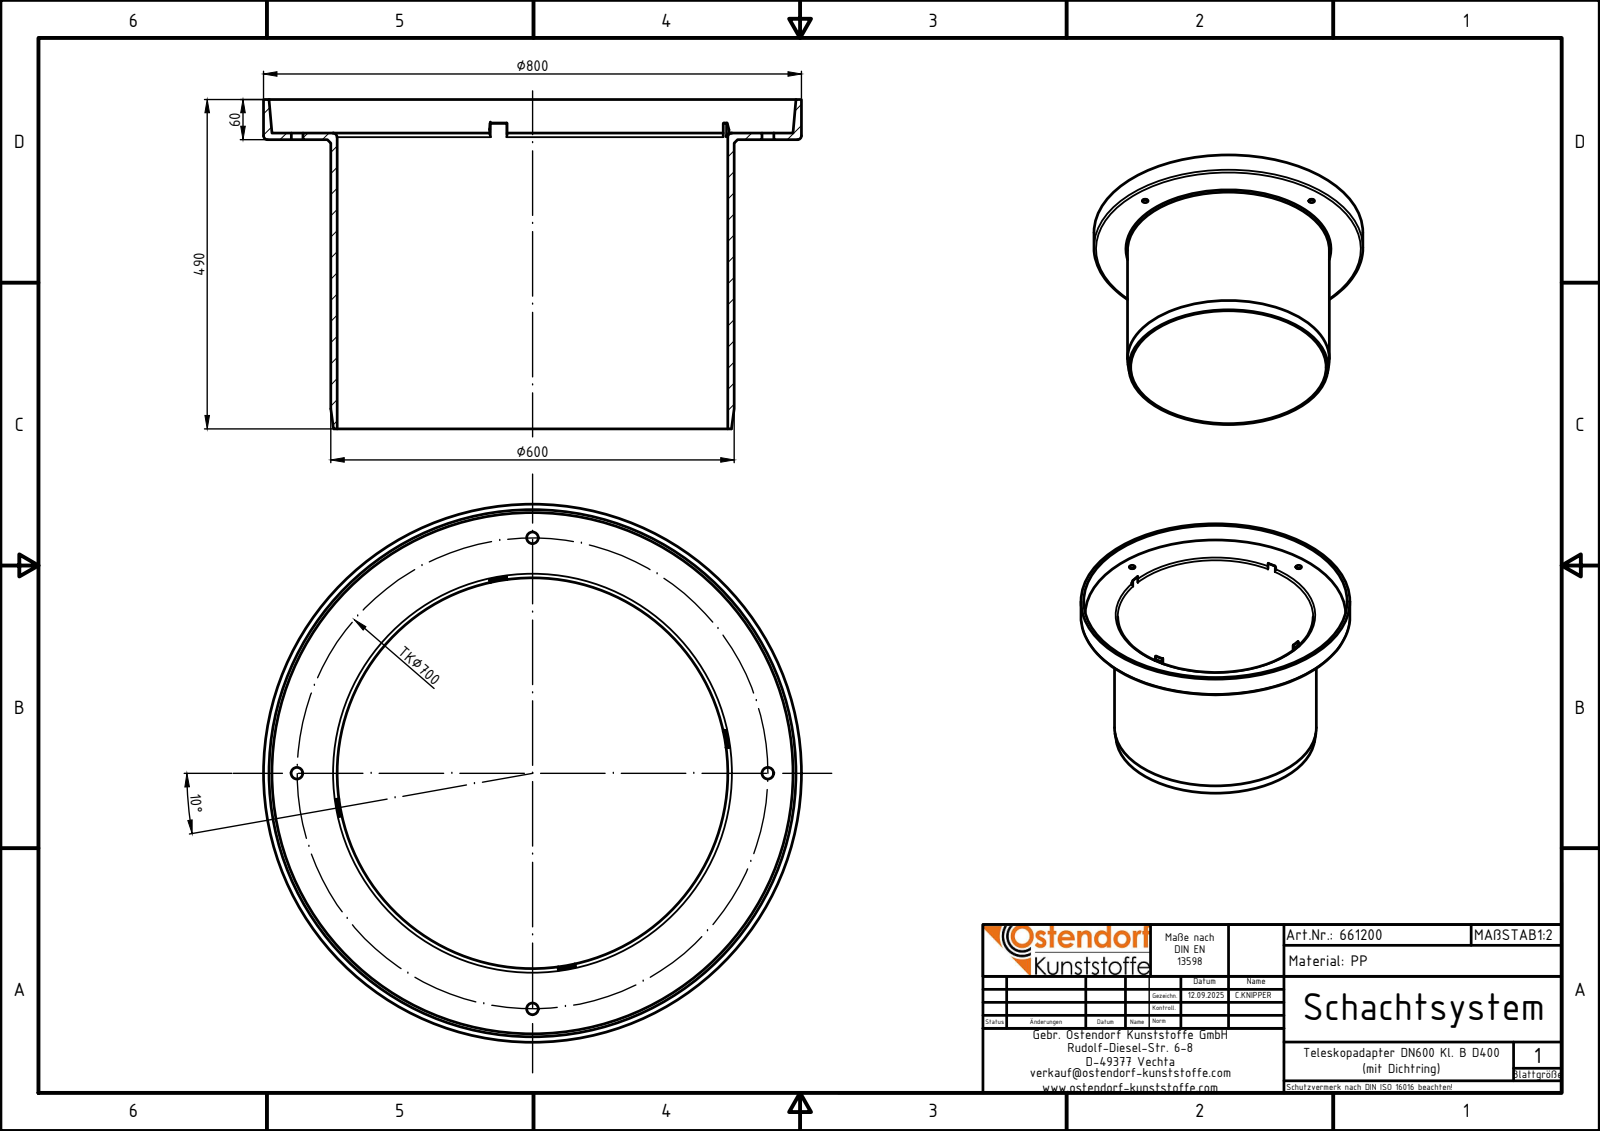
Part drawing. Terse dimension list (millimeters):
name: 661200z
written by: Autodesk Inventor 2024 (AUTOMOTIVE_DESIGN)
unit: mm
bodies: 1 solid, 120 faces (16 planar, 35 cylindrical, 69 other)
size: 800 × 800 × 490
volume: 11 100 000 mm³; area: 2 331 000 mm²
holes: 4× ⌀17.5, 1× ⌀581
bosses: 1× ⌀800, 1× ⌀600
rounds: 24× R0.5, 1× R294.7
face distances: 10, 60, 50, 430, 440, 490, 455, 25, 15, 35
hole spacings: 350, 494.97, 700
